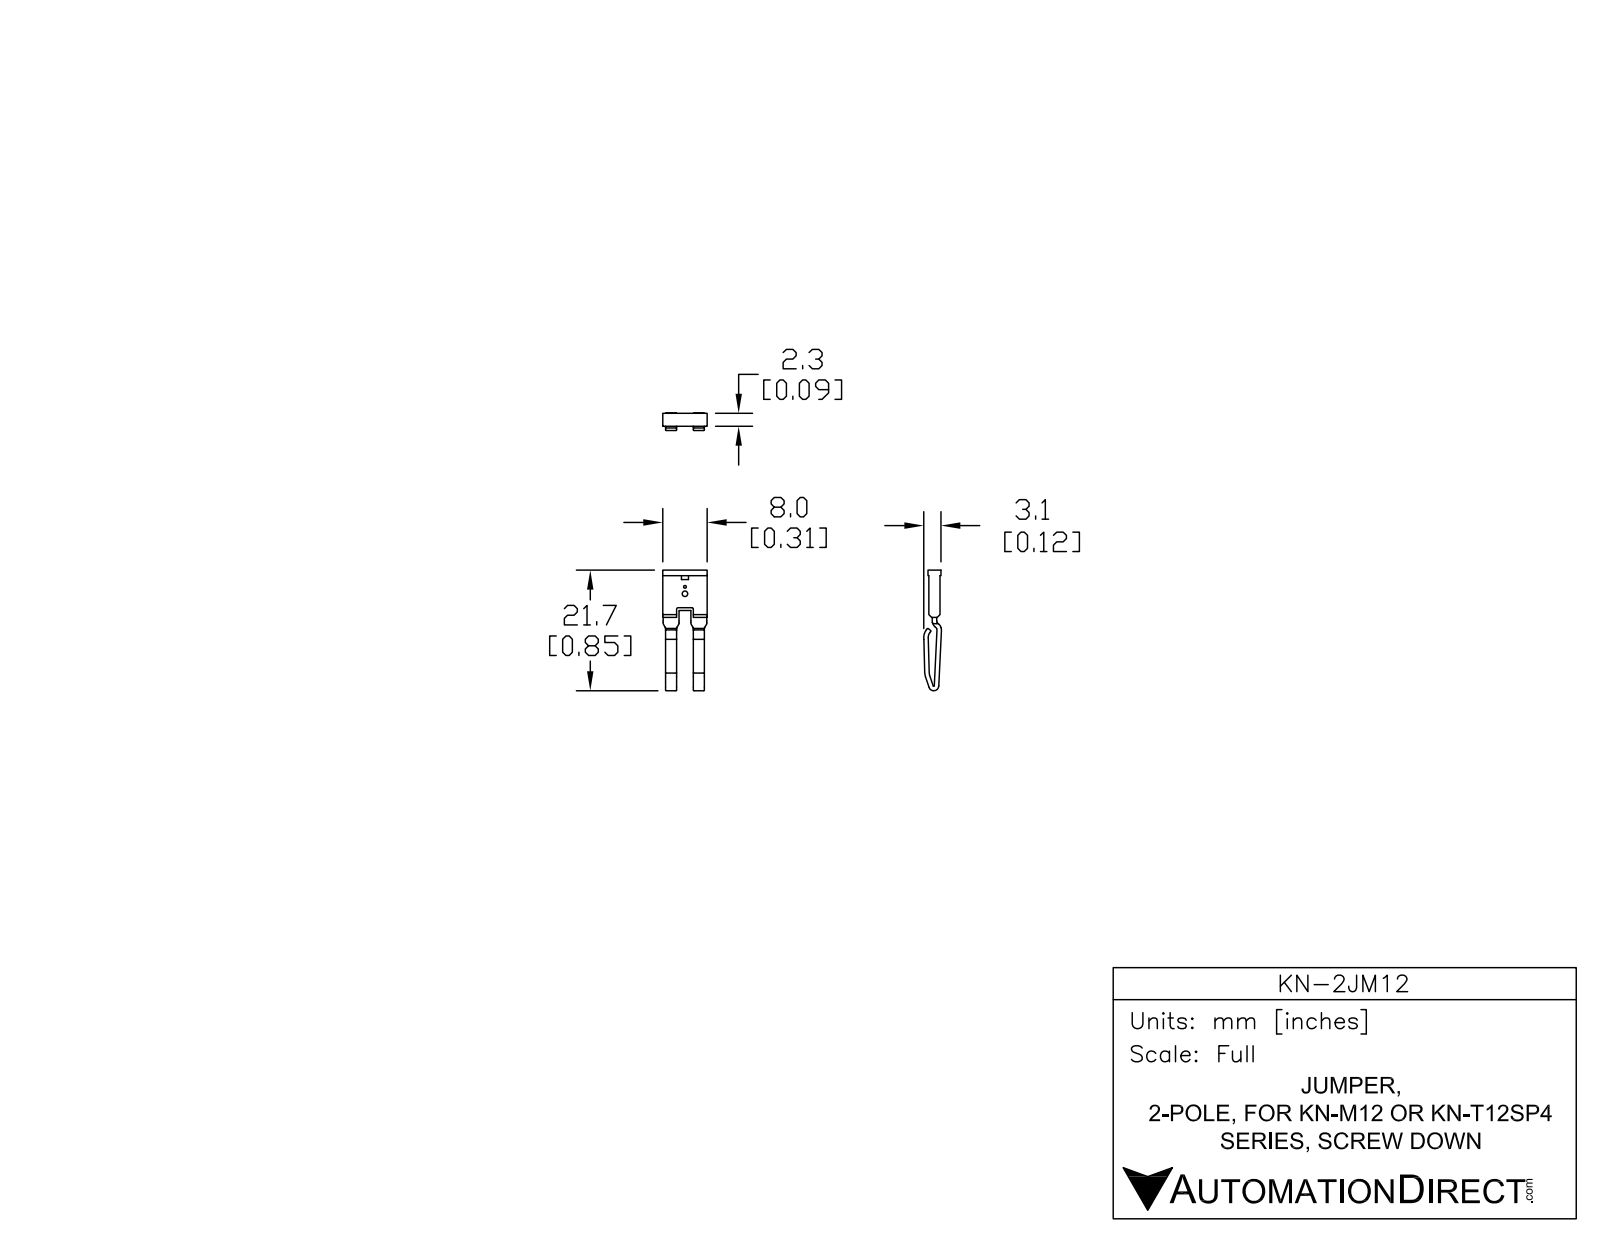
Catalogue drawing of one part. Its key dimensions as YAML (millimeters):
part_name: "KN-2JM12"
step_written_by: "SolidWorks 2014 (AUTOMOTIVE_DESIGN)"
units: millimeters
bodies: {solids: 1, faces: 224, planar: 68, cylindrical: 86, other: 70}
overall_size: [21.69, 8, 3.19]
volume: 203
surface_area: 494
round_holes:
  - {diameter: 0.5, count: 1}
  - {diameter: 1, count: 1}
partial_cylinders:
  - {radius: 0.12, count: 50}
  - {radius: 0.25, count: 2}
  - {radius: 0.6, count: 2}
  - {radius: 1.4, count: 2}
  - {radius: 1.6, count: 2}
  - {radius: 2.4, count: 2}
  - {radius: 0.1, count: 1}
  - {radius: 0.9, count: 1}
face_to_face_distances: [2, 0.8, 0.5, 2.5, 5.5, 7.5, 5, 8, 3, 1]
hole_center_spacings: [1.25]
